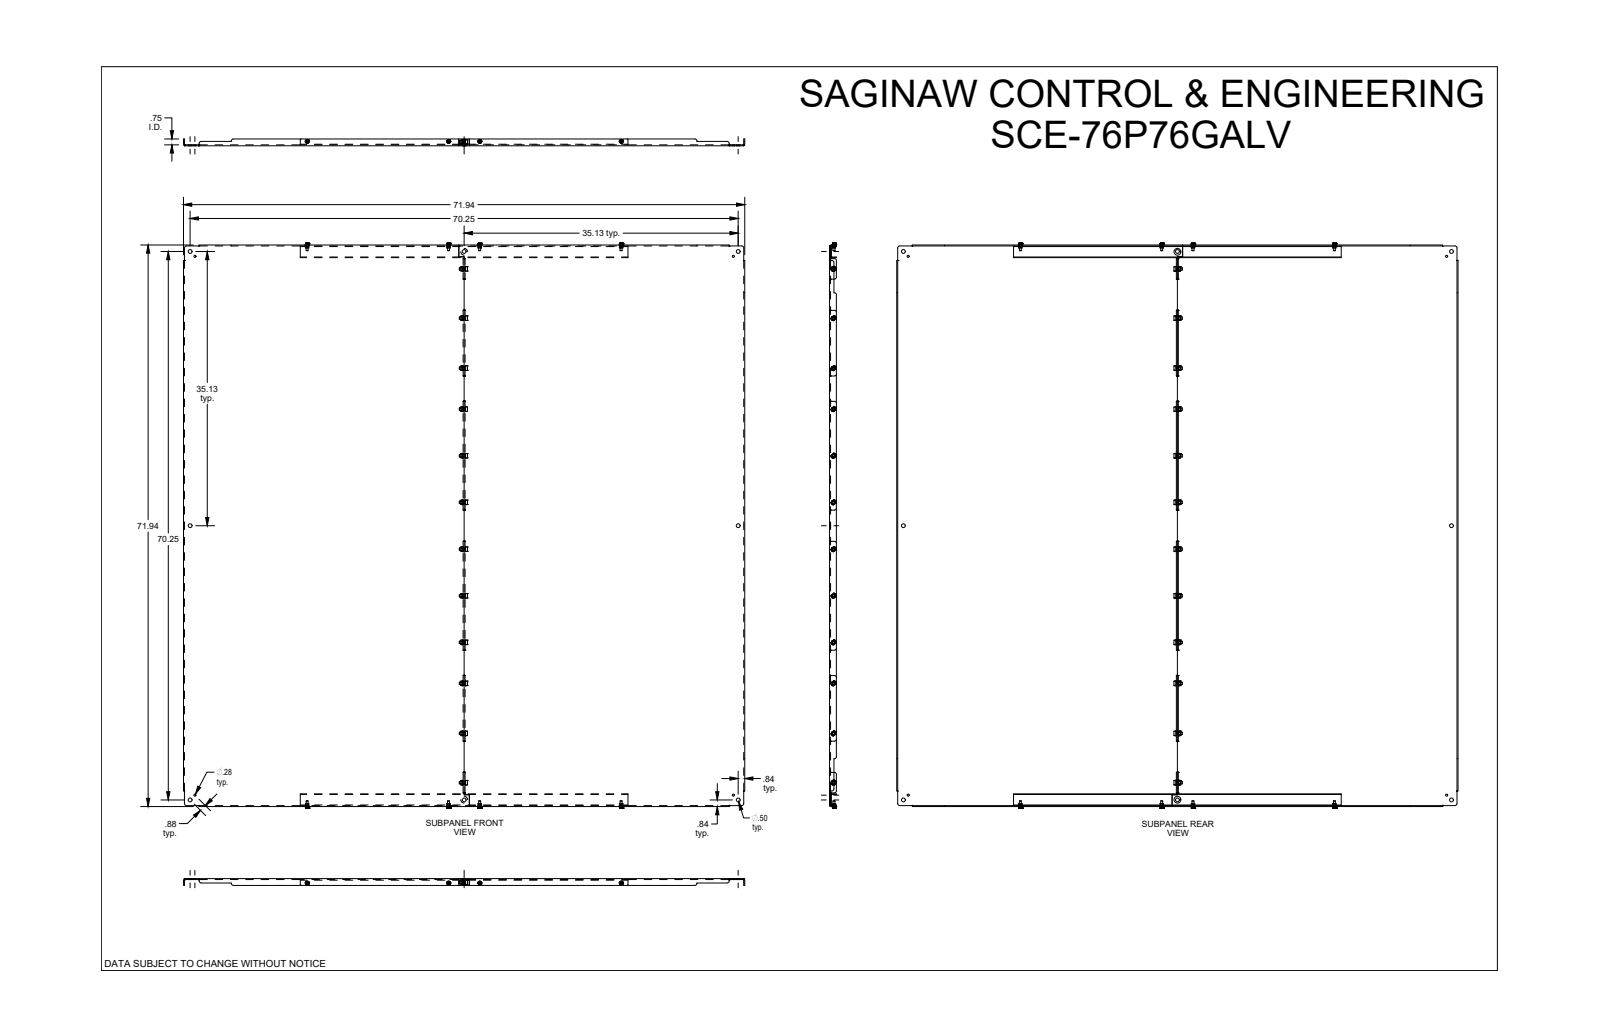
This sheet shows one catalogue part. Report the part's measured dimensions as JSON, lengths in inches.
{"part_name": "SCE-76P76GALV", "step_written_by": "SolidWorks 2019 (CONFIG_CONTROL_DESIGN)", "units": "inches", "bodies": {"solids": 44, "faces": 1922, "planar": 528, "cylindrical": 478, "other": 916}, "overall_size": [72.386, 71.938, 0.875], "volume_in3": 696.5, "surface_area_in2": 11403, "round_holes": [[0.312, 12], [0.375, 12], [0.5, 8], [0.25, 4], [0.308, 4], [0.344, 4], [0.281, 3], [0.875, 2], [0.28, 1]], "round_bosses_or_shafts": [[0.31, 12], [0.5, 4], [0.44, 4], [0.343, 4], [0.248, 4]], "partial_cylinders_radius": [[0.01, 200], [0.25, 24], [0.06, 16], [0.172, 8], [0.112, 6], [0.237, 6], [0.08, 4], [0.158, 4]], "face_to_face_distances": [0.125, 0.125, 0.078, 0.203, 35.844, 71.813, 71.687, 1.422, 70.187, 0.078], "hole_center_spacings": [35.125, 34.512, 69.634, 77.712, 78.542, 0.875, 34.511, 35.125]}
